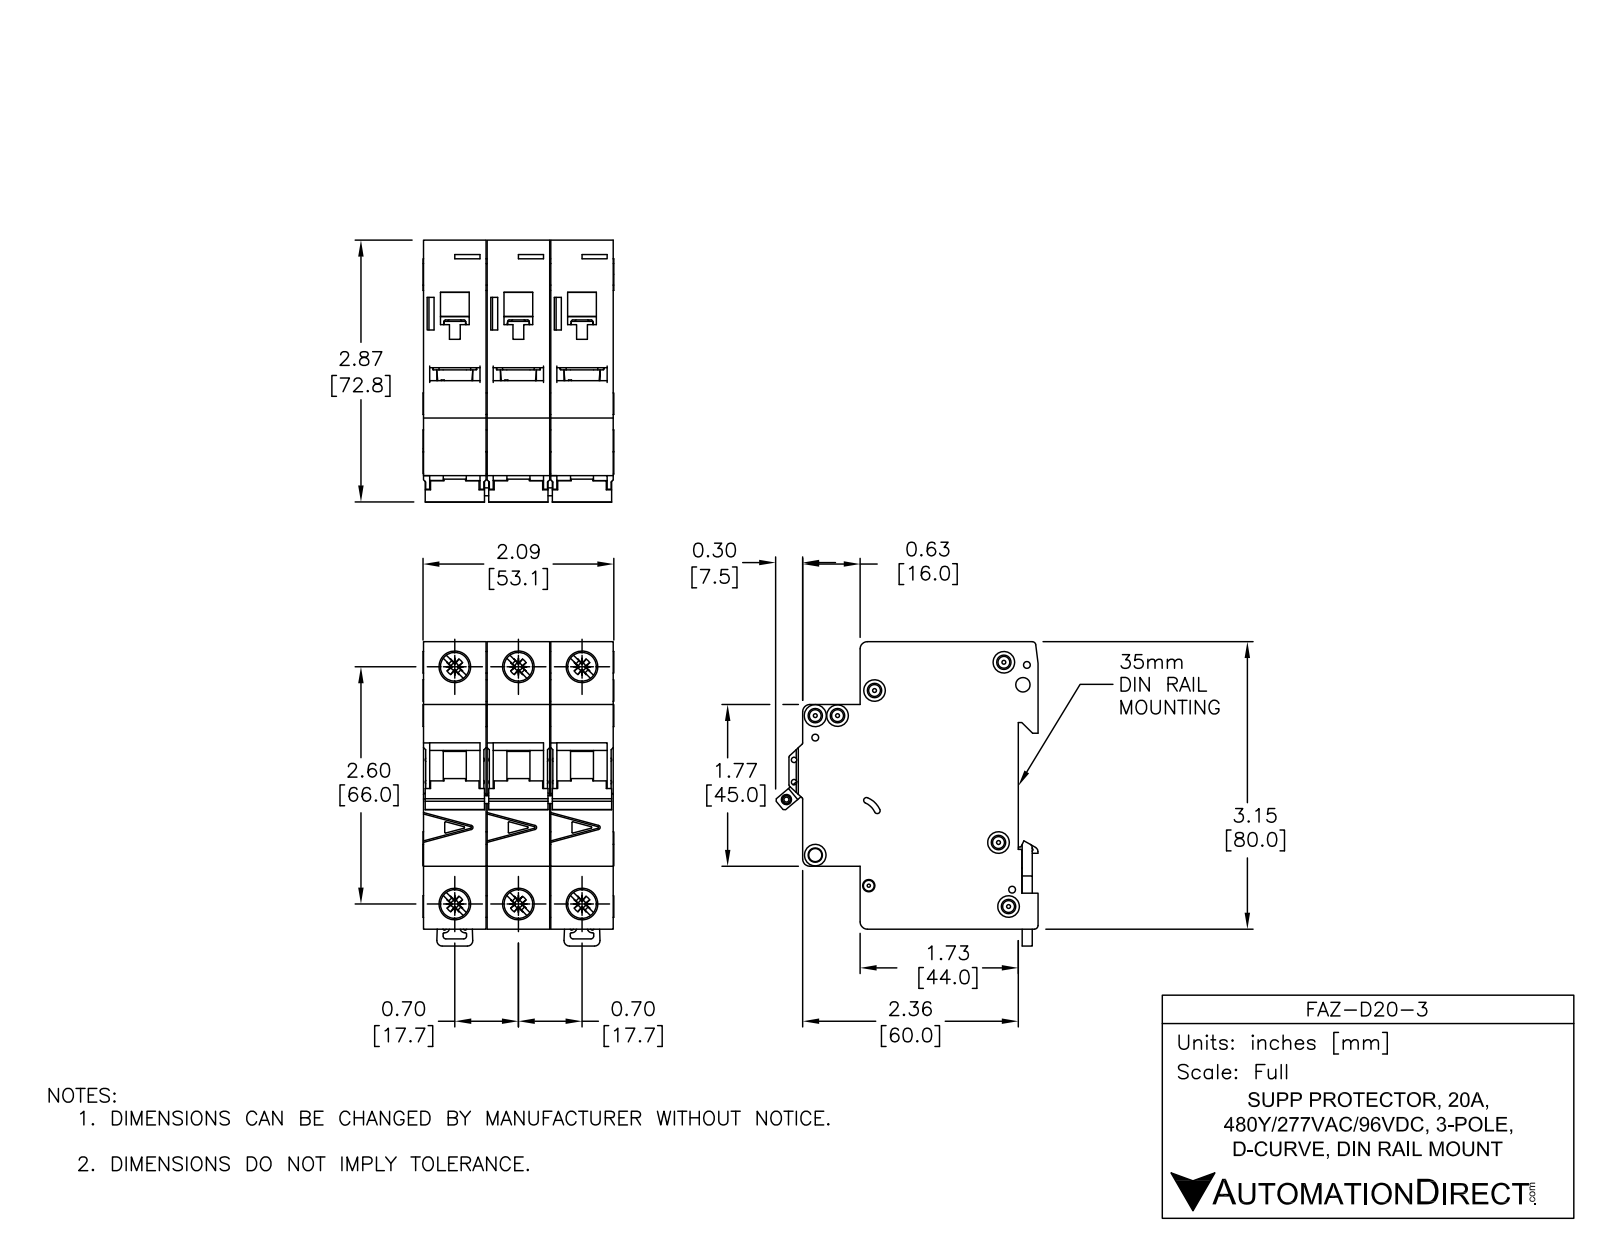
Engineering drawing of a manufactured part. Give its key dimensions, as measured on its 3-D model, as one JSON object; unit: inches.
{"part_name": "FAZ-D20-3", "step_written_by": "SolidWorks 2014 (AUTOMOTIVE_DESIGN)", "units": "inches", "bodies": {"solids": 11, "faces": 1650, "planar": 697, "cylindrical": 590, "other": 363}, "overall_size": [3.338, 2.876, 2.091], "volume_in3": 13.71, "surface_area_in2": 89.98, "round_holes": [[0.142, 6], [0.323, 4], [0.075, 3], [0.043, 2], [0.059, 2], [0.157, 2], [0.281, 2], [0.085, 1], [0.087, 1], [0.1, 1], [0.13, 1], [0.134, 1]], "round_bosses_or_shafts": [[0.236, 4], [0.098, 3], [0.323, 2]], "partial_cylinders_radius": [[0.01, 68], [0.02, 25], [0.039, 12], [0.079, 12], [0.008, 11], [0.071, 3], [0.031, 2], [0.118, 2]], "face_to_face_distances": [0.697, 0.689, 1.394, 1.386, 2.083, 0.705, 3.129, 0.217, 1.949, 1.732], "hole_center_spacings": [0.697, 2.69, 2.598, 0.244, 0.537, 1.394, 2.948, 0.189]}
